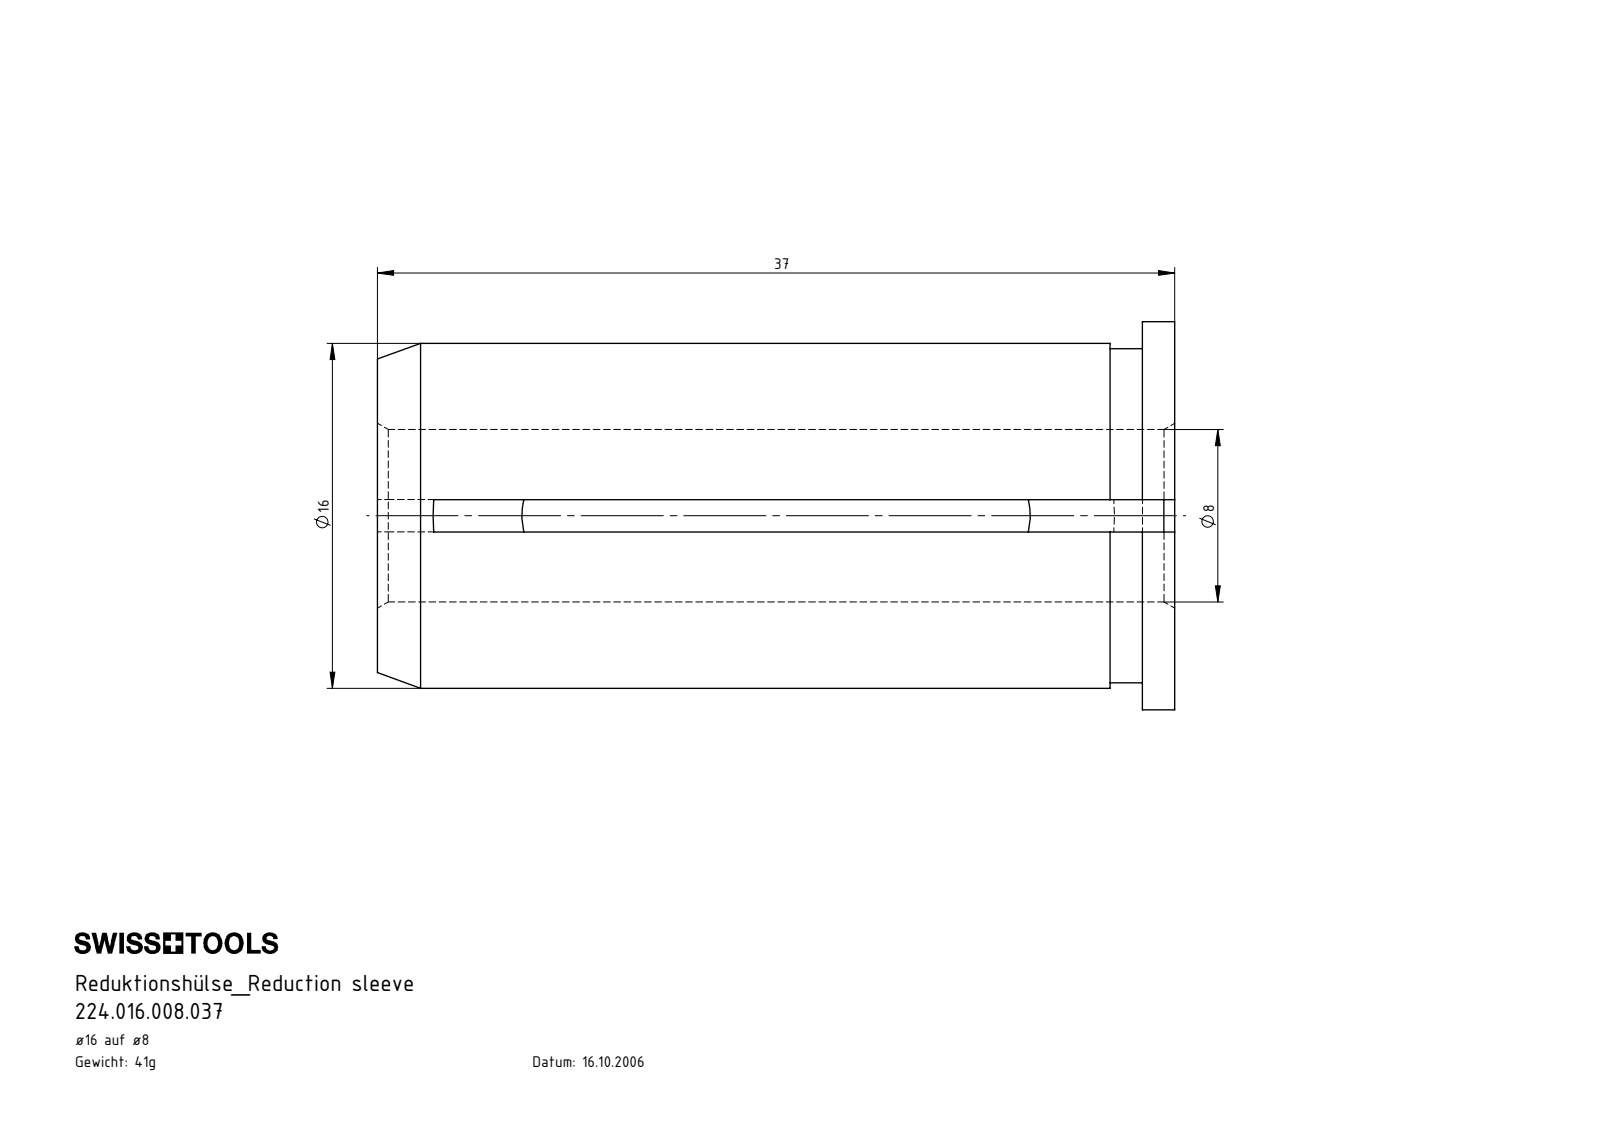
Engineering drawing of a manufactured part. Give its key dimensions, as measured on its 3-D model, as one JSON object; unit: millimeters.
{"part_name": "U08.U16.001.037", "step_written_by": "SolidWorks 2017 (AUTOMOTIVE_DESIGN)", "units": "millimeters", "bodies": {"solids": 1, "faces": 18, "planar": 9, "cylindrical": 6, "other": 3}, "overall_size": [37, 18, 17.97], "volume_mm3": 5211, "surface_area_mm2": 3518, "round_holes": [[8, 1]], "round_bosses_or_shafts": [[18, 1], [16, 1], [15.5, 1]], "partial_cylinders_radius": [[31.5, 2]], "face_to_face_distances": [1.5, 37, 35.5, 34, 3]}
